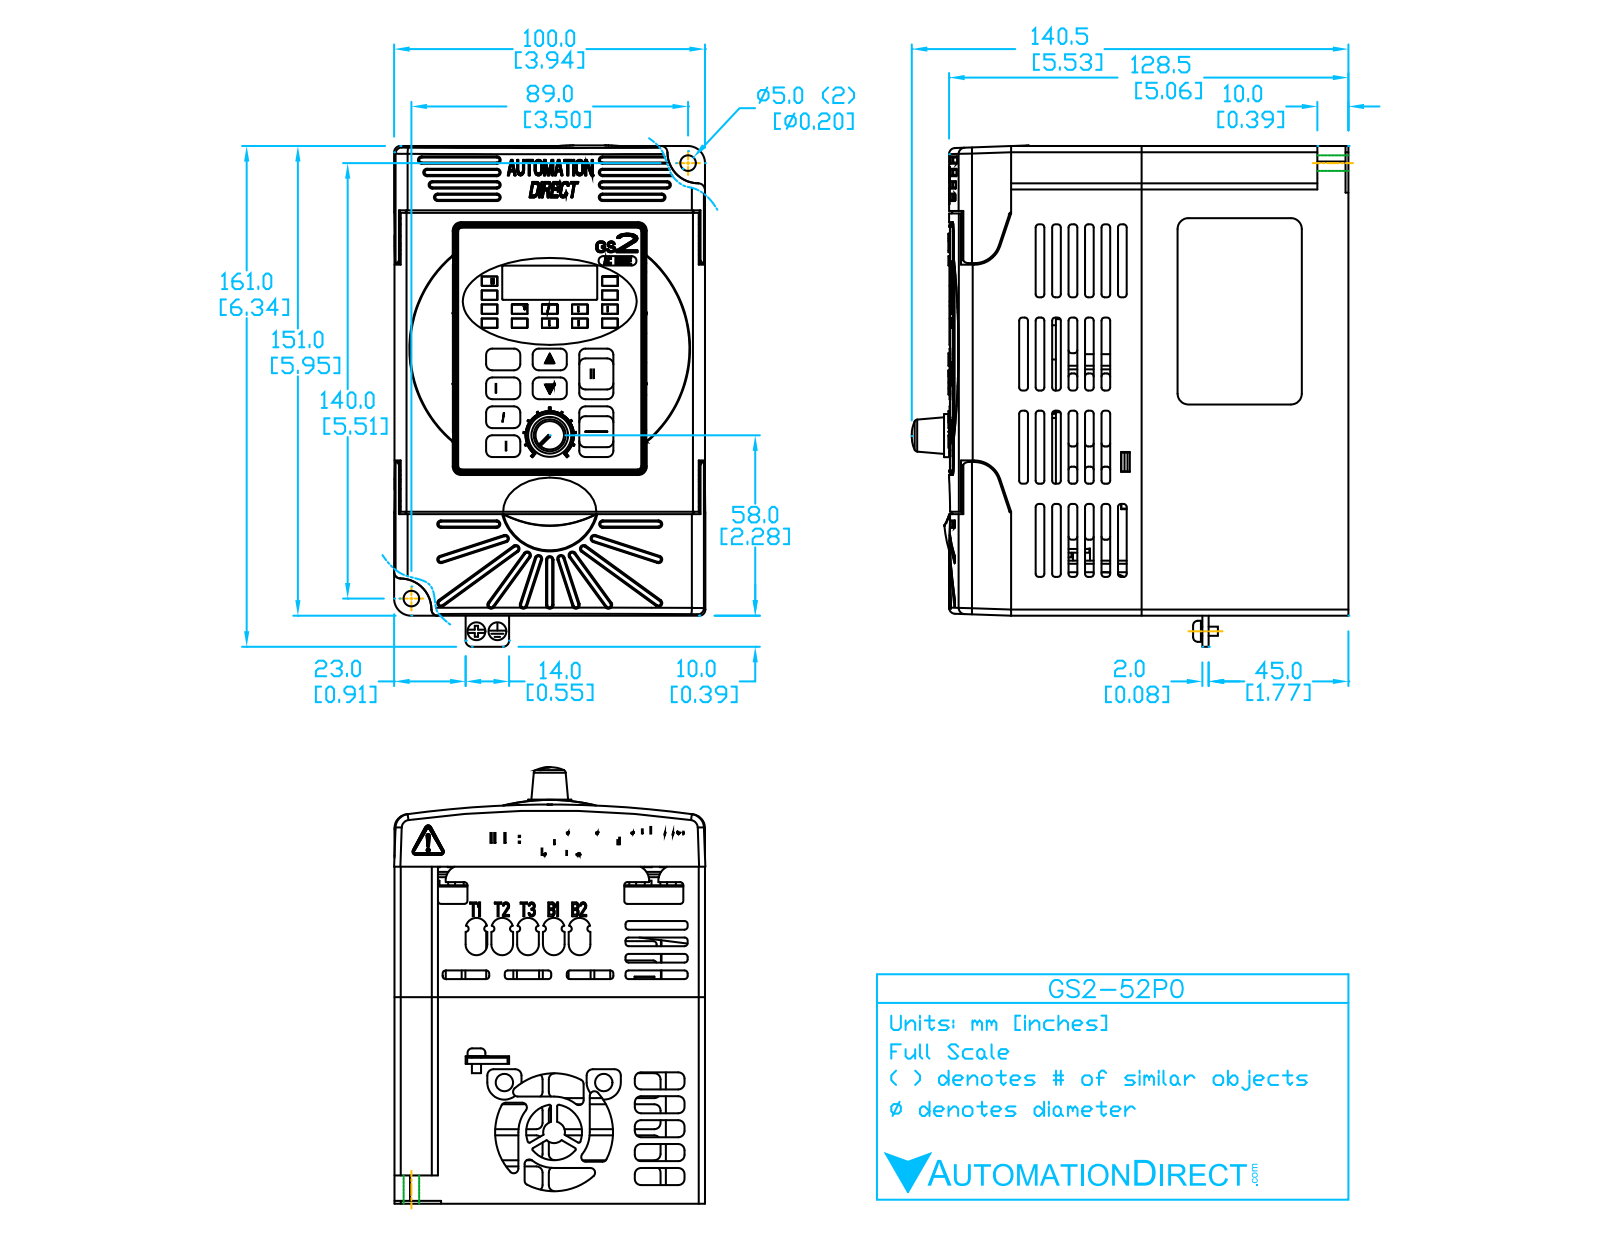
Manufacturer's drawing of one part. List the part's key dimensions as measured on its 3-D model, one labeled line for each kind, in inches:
Part name (STEP PRODUCT): GS2-52P0
STEP written by: SolidWorks 2013 (AUTOMOTIVE_DESIGN)
Units: inches
Bodies: 1 solid, 748 faces (332 planar, 220 cylindrical, 196 other)
Overall size (bounding box): 6.345 × 5.495 × 3.94
Volume: 112.9 in³ · Surface area: 196.7 in²
Round holes (diameter × count): ⌀0.2 ×2, ⌀0.7 ×1, ⌀1.46 ×1
Round bosses / shafts (diameter × count): ⌀0.545 ×1, ⌀0.22 ×1, ⌀0.15 ×1
Partial cylindrical surfaces — rounded edges, fillets, slot ends (radius × count): R0.04 ×40, R0.06 ×16, R0.03 ×14, R0.125 ×10, R0.03 ×8, R0.045 ×6, R0.2 ×6, R0.1 ×4
Main face-to-face distances: 3.94, 5.95, 4.256, 4.266, 0.015, 5.935, 0.03, 0.761, 3.179, 0.03
Hole centre spacings: 6.528
